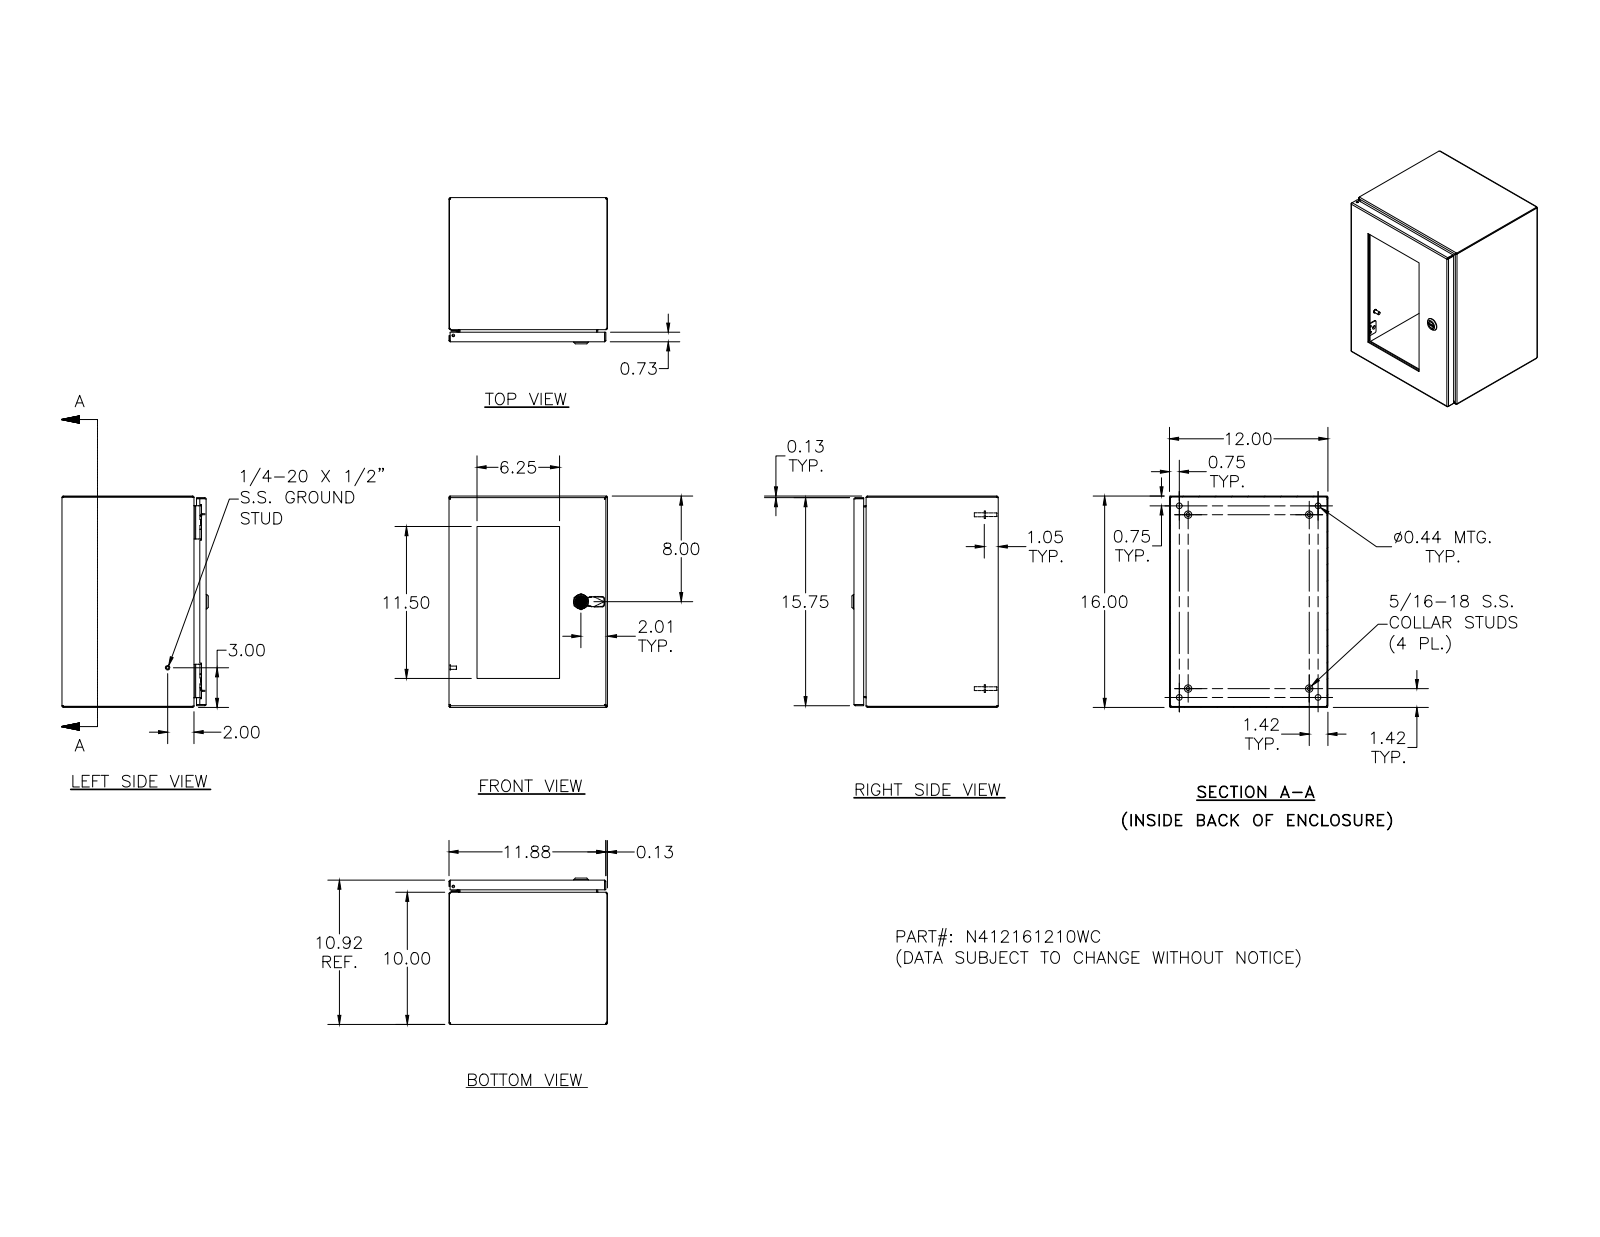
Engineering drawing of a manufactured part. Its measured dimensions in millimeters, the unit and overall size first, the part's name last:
Units: millimetres
Overall size (bounding box): 406.4 × 304.8 × 281.3
Round holes (diameter × count): ⌀4 ×12, ⌀7.1 ×10, ⌀4.8 ×5, ⌀2.4 ×4, ⌀3.9 ×4, ⌀4.2 ×4, ⌀4.4 ×4, ⌀11.1 ×4, ⌀4.7 ×1, ⌀5 ×1, ⌀8 ×1, ⌀10 ×1
Round bosses / shafts (diameter × count): ⌀8.6 ×10, ⌀6.4 ×10, ⌀4.8 ×10, ⌀14.3 ×4, ⌀9.1 ×4, ⌀8.1 ×4, ⌀7.6 ×4, ⌀7 ×4
Partial cylindrical surfaces — rounded edges, fillets, slot ends (radius × count): R0.8 ×34, R0.3 ×30, R1.3 ×26, R2.7 ×24, R0.4 ×18, R3.2 ×16, R0.5 ×13, R0.8 ×8
Main face-to-face distances: 1.9, 302.9, 275.4, 404.5, 273.5, 304.8, 301, 402.6, 406.4, 277.3
Hole centre spacings: 101.6, 304.8, 158, 215.9, 218.1, 301.3, 190.5, 12.7
Volume: 1 629 000 mm³ · Surface area: 1 479 000 mm²
Bodies: 57 solids, 1827 faces (687 planar, 593 cylindrical, 547 other)
Part name (STEP PRODUCT): N412161210WC
STEP written by: SolidWorks 2018 (AUTOMOTIVE_DESIGN)
